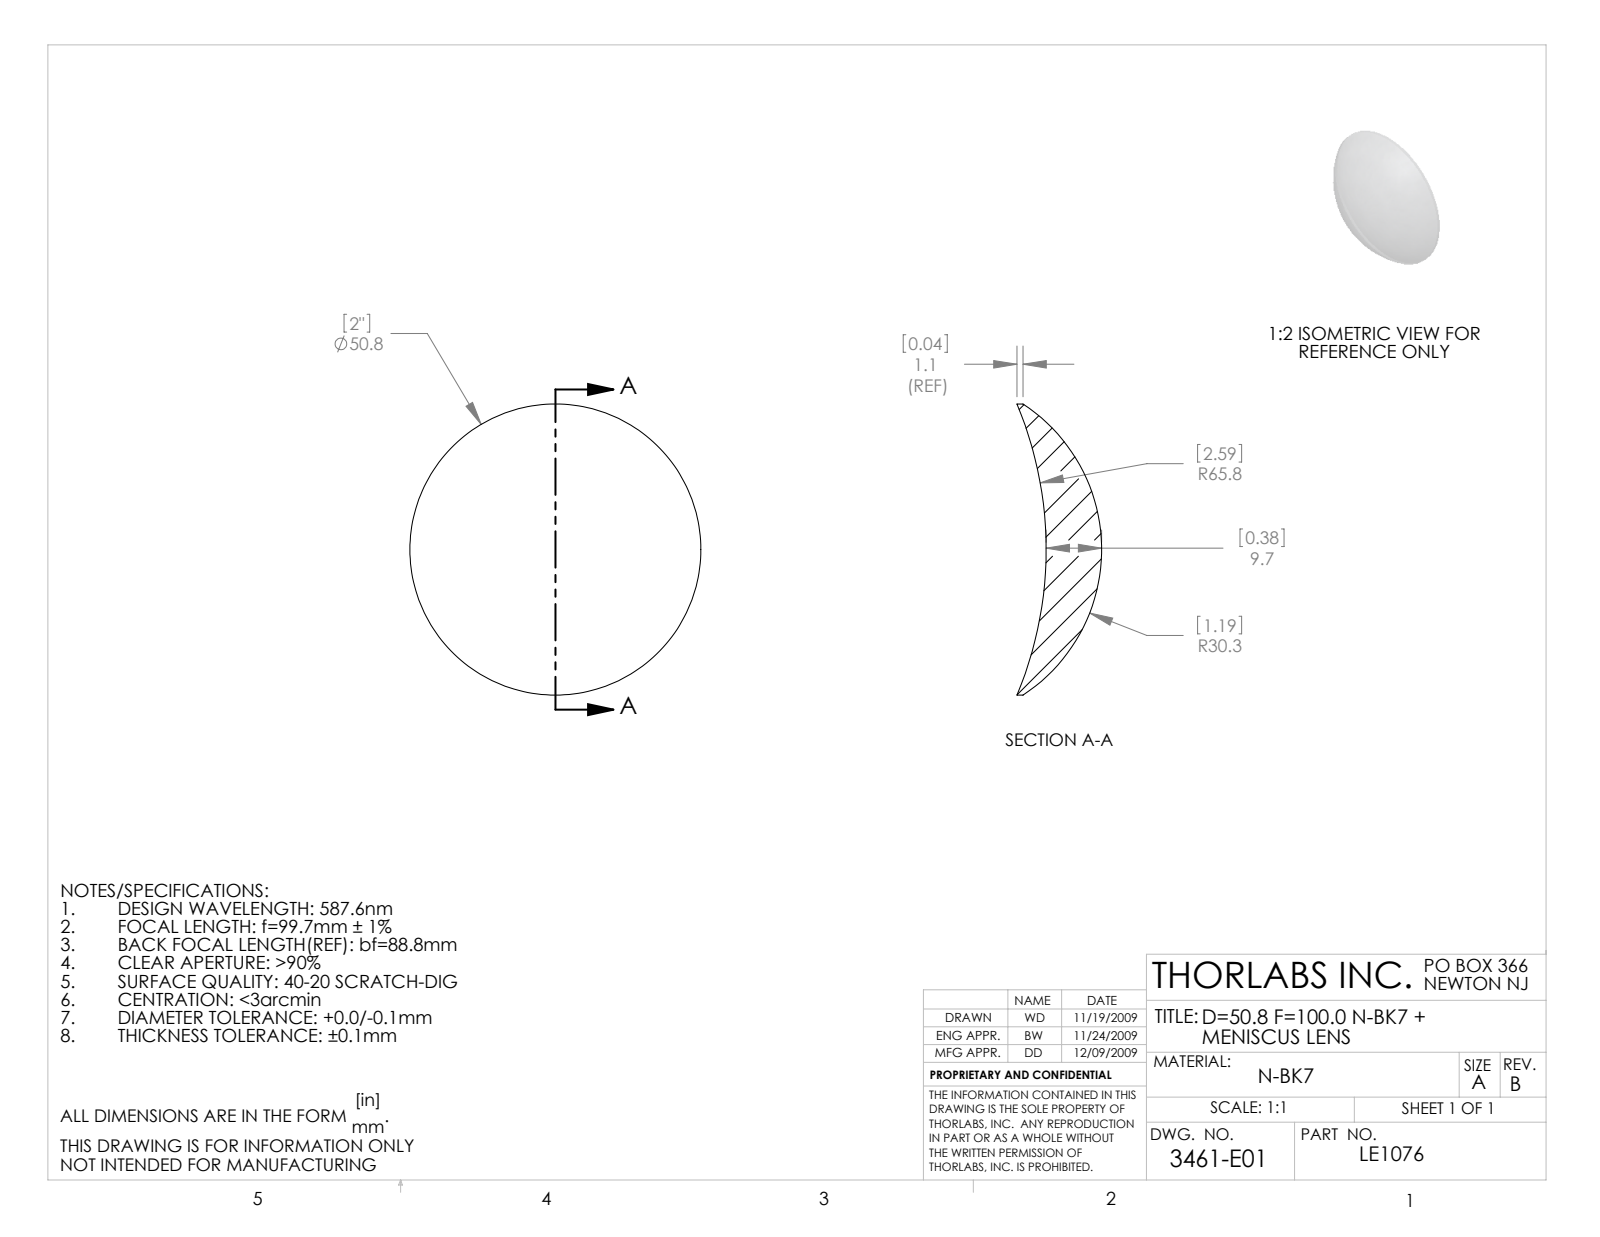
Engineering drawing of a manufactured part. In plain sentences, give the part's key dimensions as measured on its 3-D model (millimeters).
The part is named "3461-E0W". Its 3-D file was written by "SolidWorks 2009 (AUTOMOTIVE_DESIGN)". It is 1 solid with 6 faces: 0 planar, 2 cylindrical and 4 other. Overall it measures 50.8 by 50.8 by 14.8 millimeters. Its volume is 12 189 cubic millimeters and its surface area 4 897 square millimeters. Round bosses or shafts: 1 of diameter 50.8.
